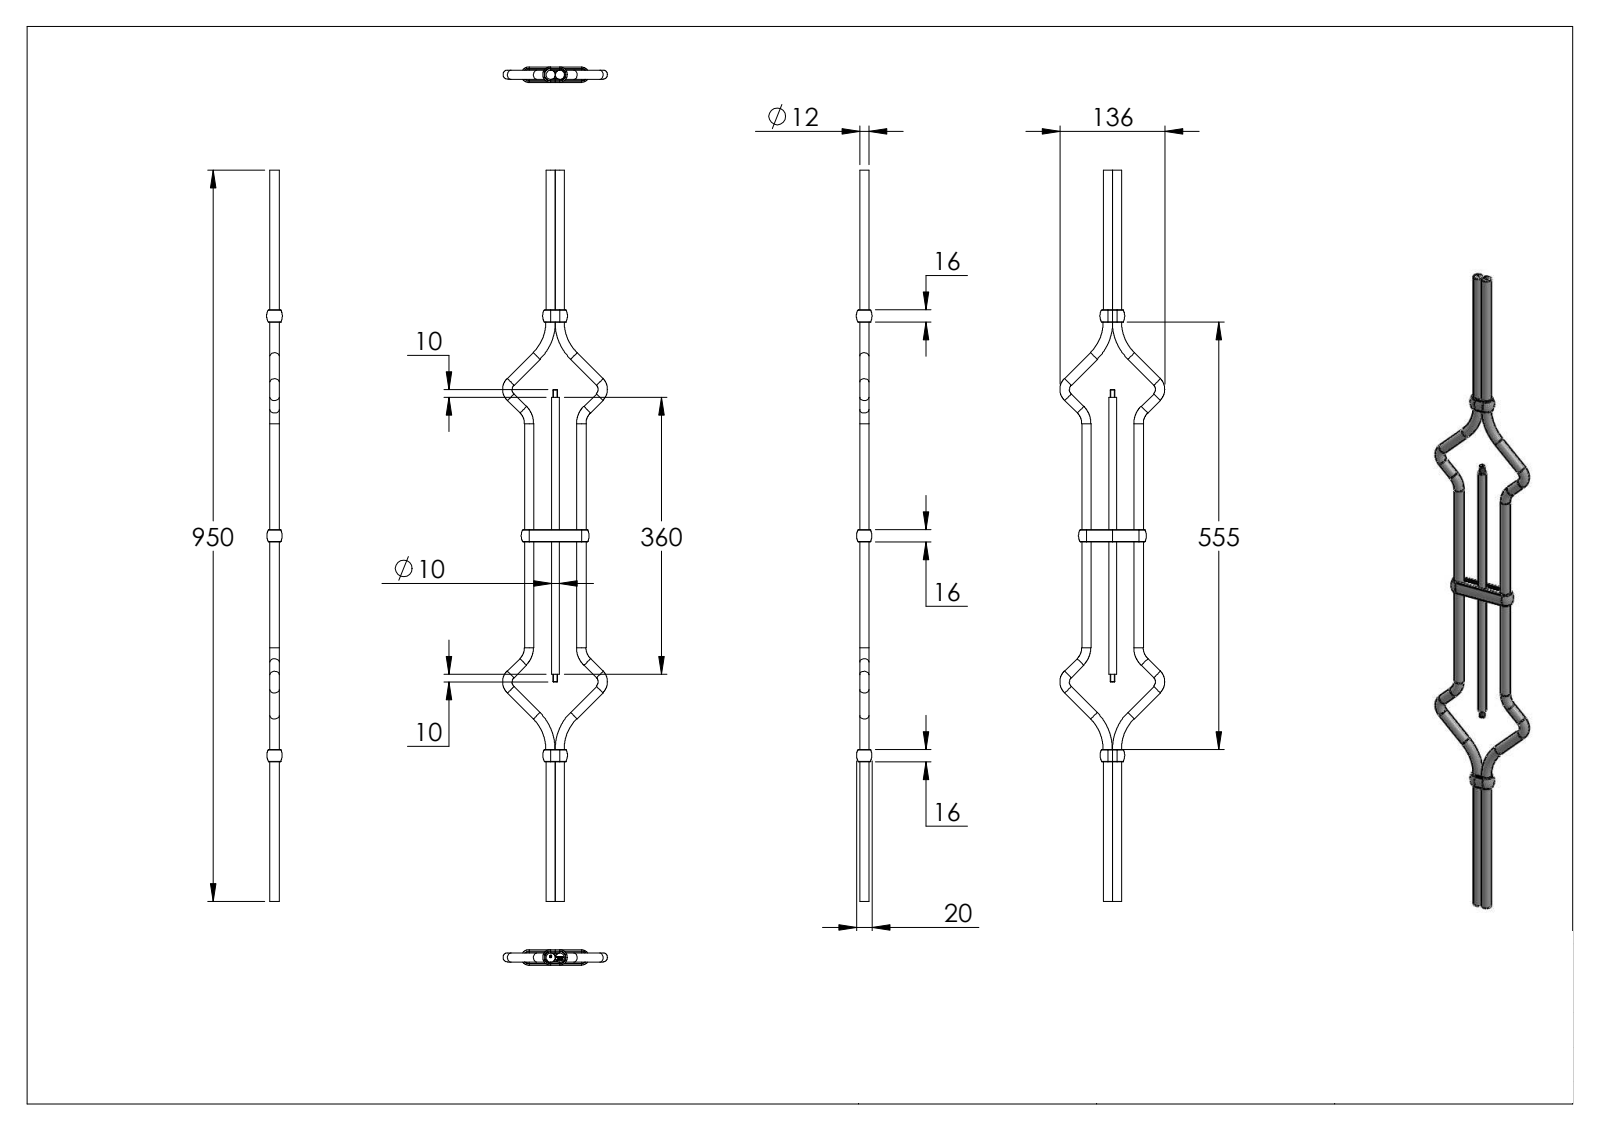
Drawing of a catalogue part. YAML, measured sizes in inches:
part_name: "56102-ST"
step_written_by: "SolidWorks 2018 (CONFIG_CONTROL_DESIGN)"
units: inches
bodies: {solids: 6, faces: 387, planar: 188, cylindrical: 52, other: 147}
overall_size: [37.402, 5.354, 0.787]
volume: 17.07
surface_area: 159
round_holes:
  - {diameter: 0.472, count: 4}
  - {diameter: 0.402, count: 1}
round_bosses_or_shafts:
  - {diameter: 0.472, count: 8}
  - {diameter: 0.394, count: 1}
  - {diameter: 0.236, count: 1}
partial_cylinders:
  - {radius: 0.039, count: 12}
  - {radius: 0.669, count: 6}
face_to_face_distances: [0.472, 0.039, 0.433, 0.394, 0.118, 0.512, 18.386, 18.504, 18.898, 19.016]
hole_center_spacings: [0.236, 1.102, 1.339, 1.575, 0.472, 2.677]
